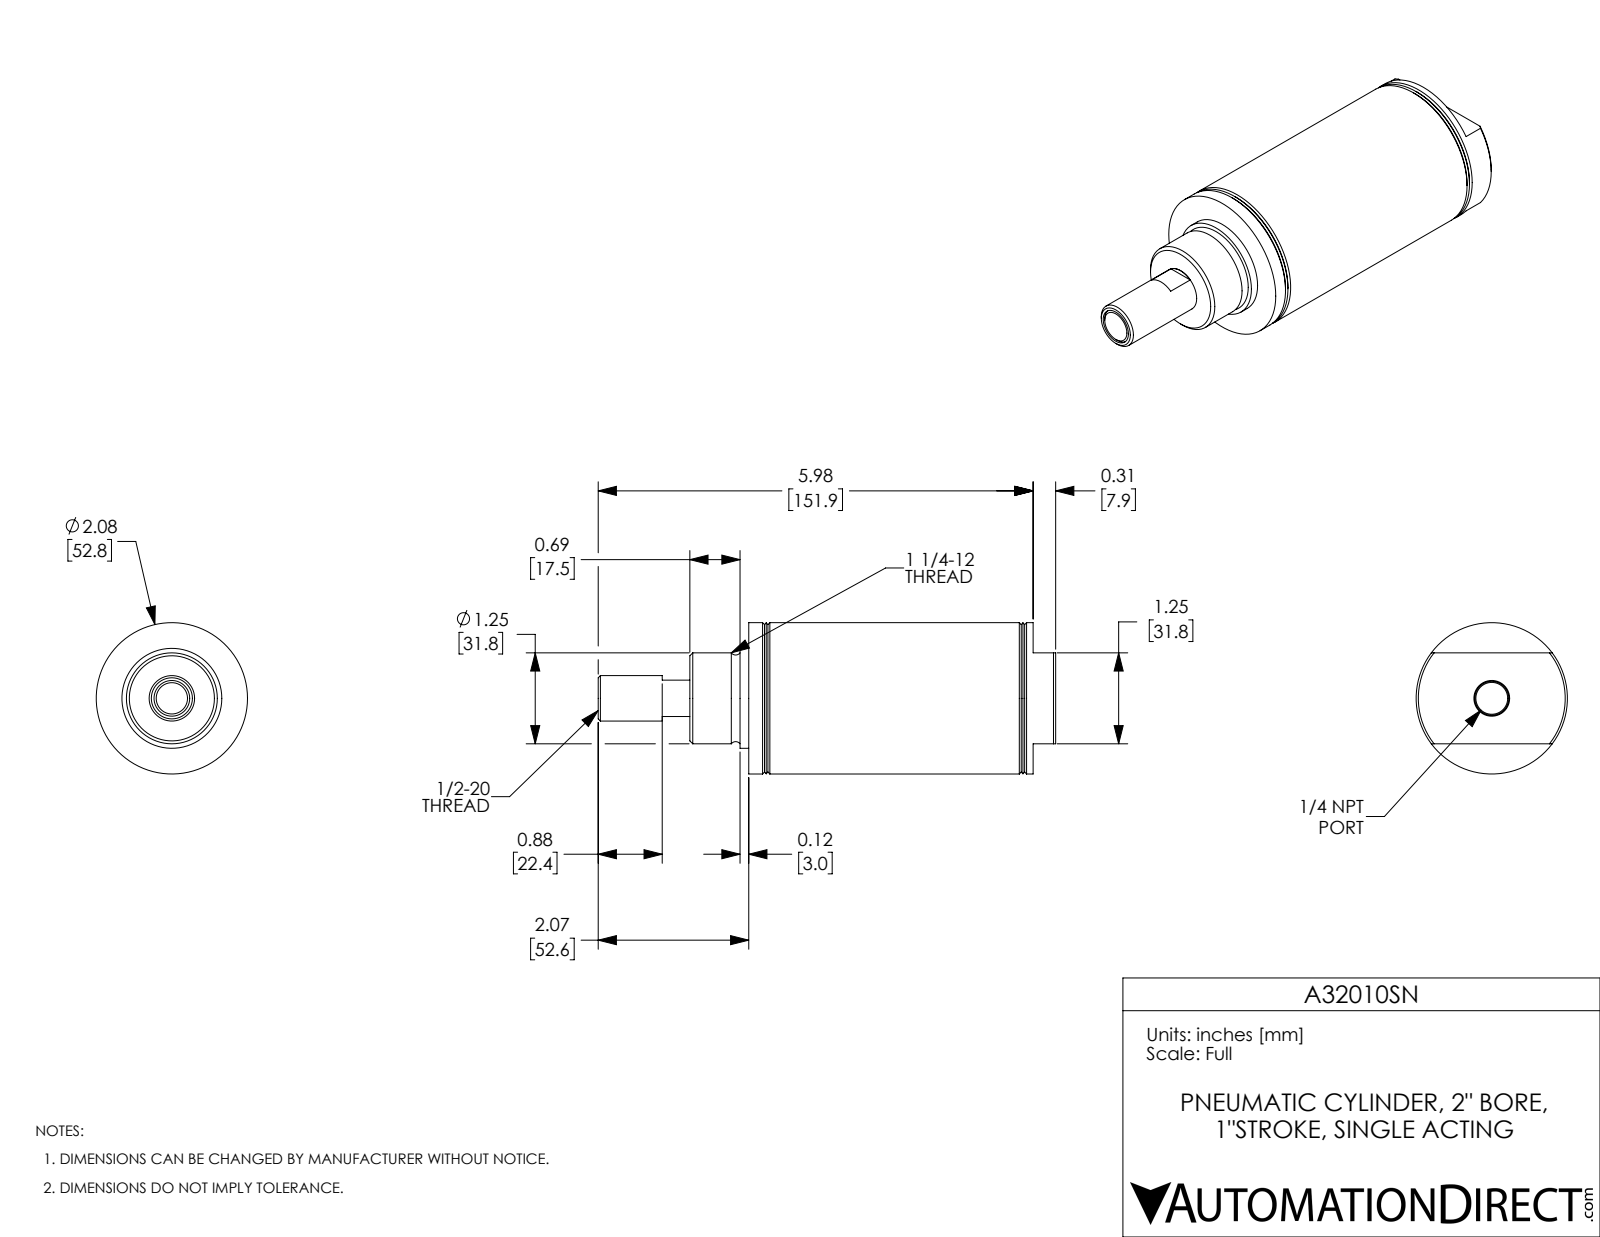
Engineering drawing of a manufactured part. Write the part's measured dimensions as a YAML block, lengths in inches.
part_name: "A32010SN-MainBody; A32010SN-Rod; A32010SN"
step_written_by: "SolidWorks 2017 (AUTOMOTIVE_DESIGN)"
units: inches
bodies: {solids: 2, faces: 76, planar: 21, cylindrical: 22, other: 33}
overall_size: [6.29, 2.08, 2.08]
volume: 15.29
surface_area: 70.12
round_holes:
  - {diameter: 0.438, count: 1}
  - {diameter: 0.491, count: 1}
  - {diameter: 0.625, count: 1}
  - {diameter: 2, count: 1}
round_bosses_or_shafts:
  - {diameter: 2.08, count: 1}
  - {diameter: 1.373, count: 1}
  - {diameter: 1.25, count: 1}
face_to_face_distances: [0.5, 1.86, 2.36, 4.22, 0.31, 1.55, 2.05, 3.91, 5.03, 4.72]
